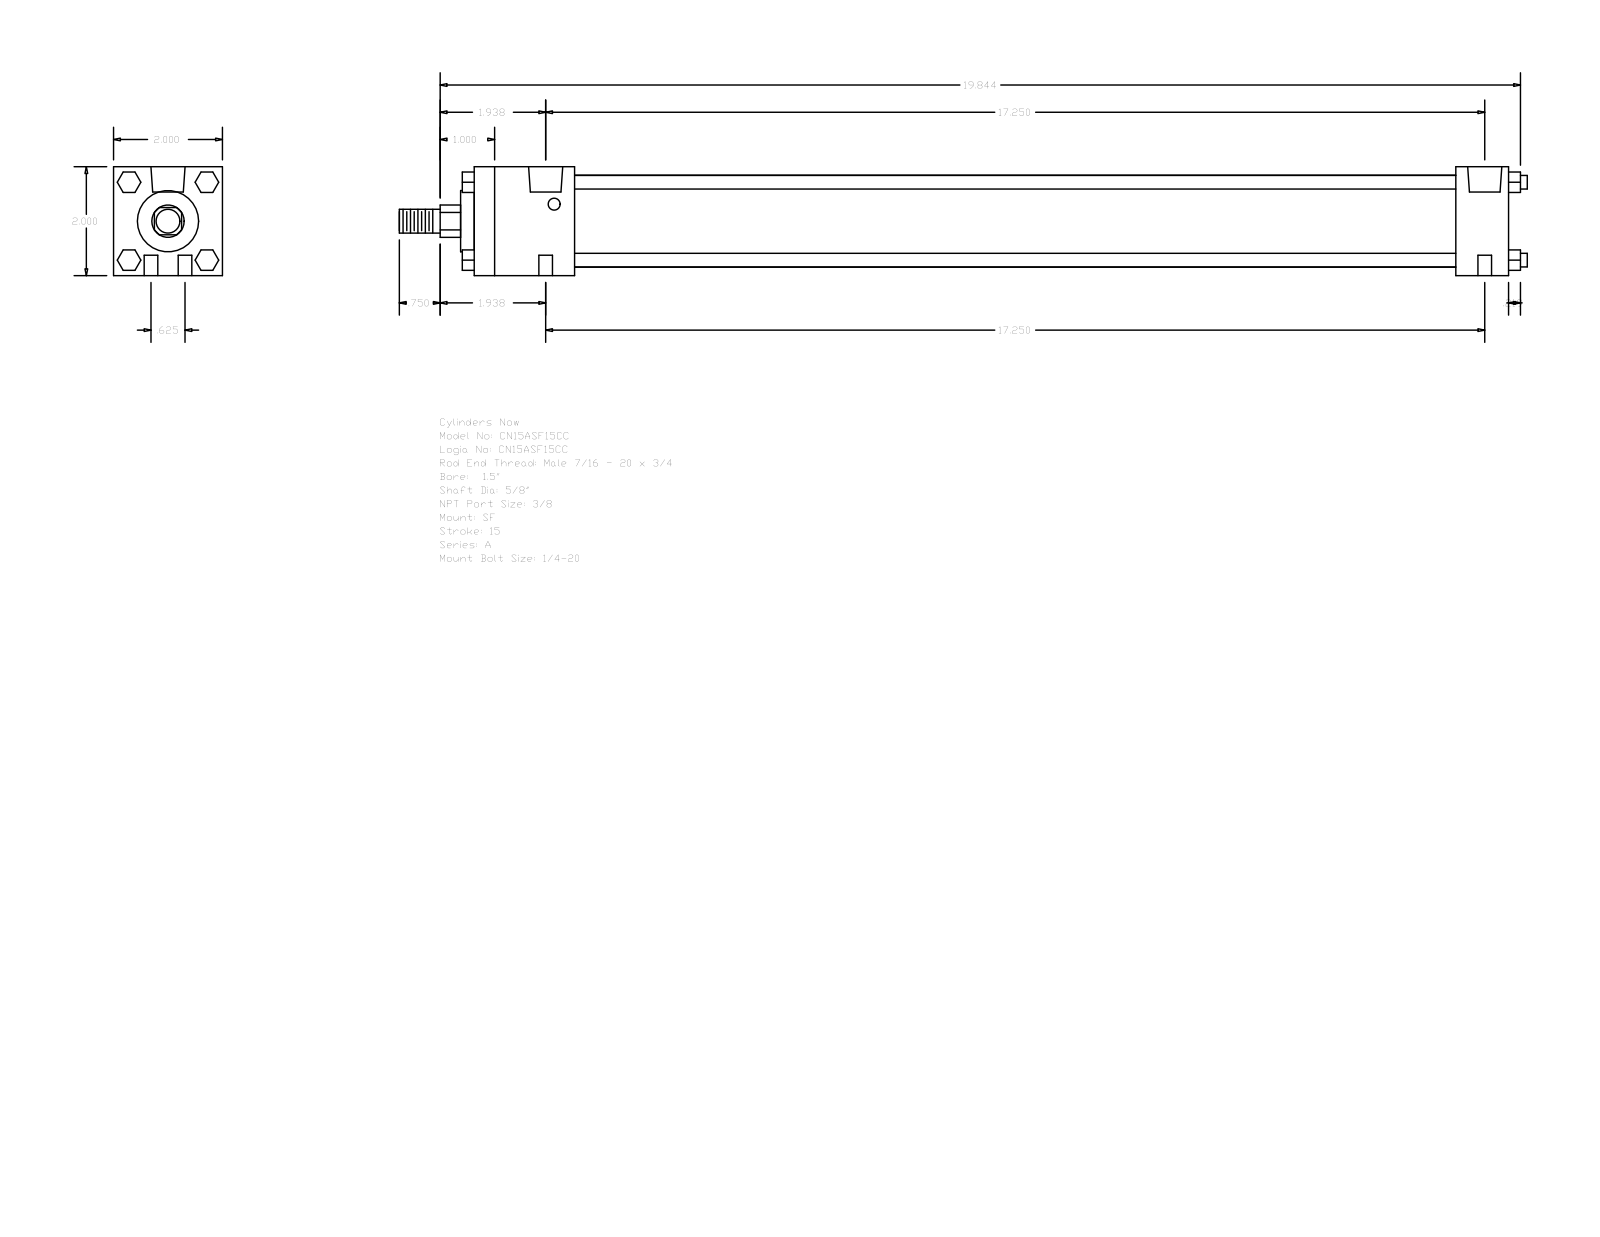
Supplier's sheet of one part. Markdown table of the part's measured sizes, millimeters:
| quantity | value |
| --- | --- |
| part name | A_SF__0150_0.625 |
| STEP written by | GSSL Pune (CONFIG_CONTROL_DESIGN) |
| units | millimeters |
| bodies | 0 solids, 124 faces (94 planar, 30 cylindrical, 0 other) |
| overall size | 526.26 × 50.8 × 50.8 |
| round holes (diameter × count) | 6.35 × 4, 5.56 × 2, 15.93 × 2 |
| round bosses / shafts (diameter × count) | 6.35 × 4, 42.93 × 1, 28.57 × 1, 15.88 × 1, 11.11 × 1 |
| partial cylindrical surfaces (radius × count) | 7.54 × 1 |
| main face-to-face distances | 50.8, 482.6, 46.83, 457.99, 411.16, 435.77, 24.61, 6.35, 9.52, 53.18 |
| hole center spacings | 7.94, 438.22, 438.15, 15.88, 438.44, 430.21 |
